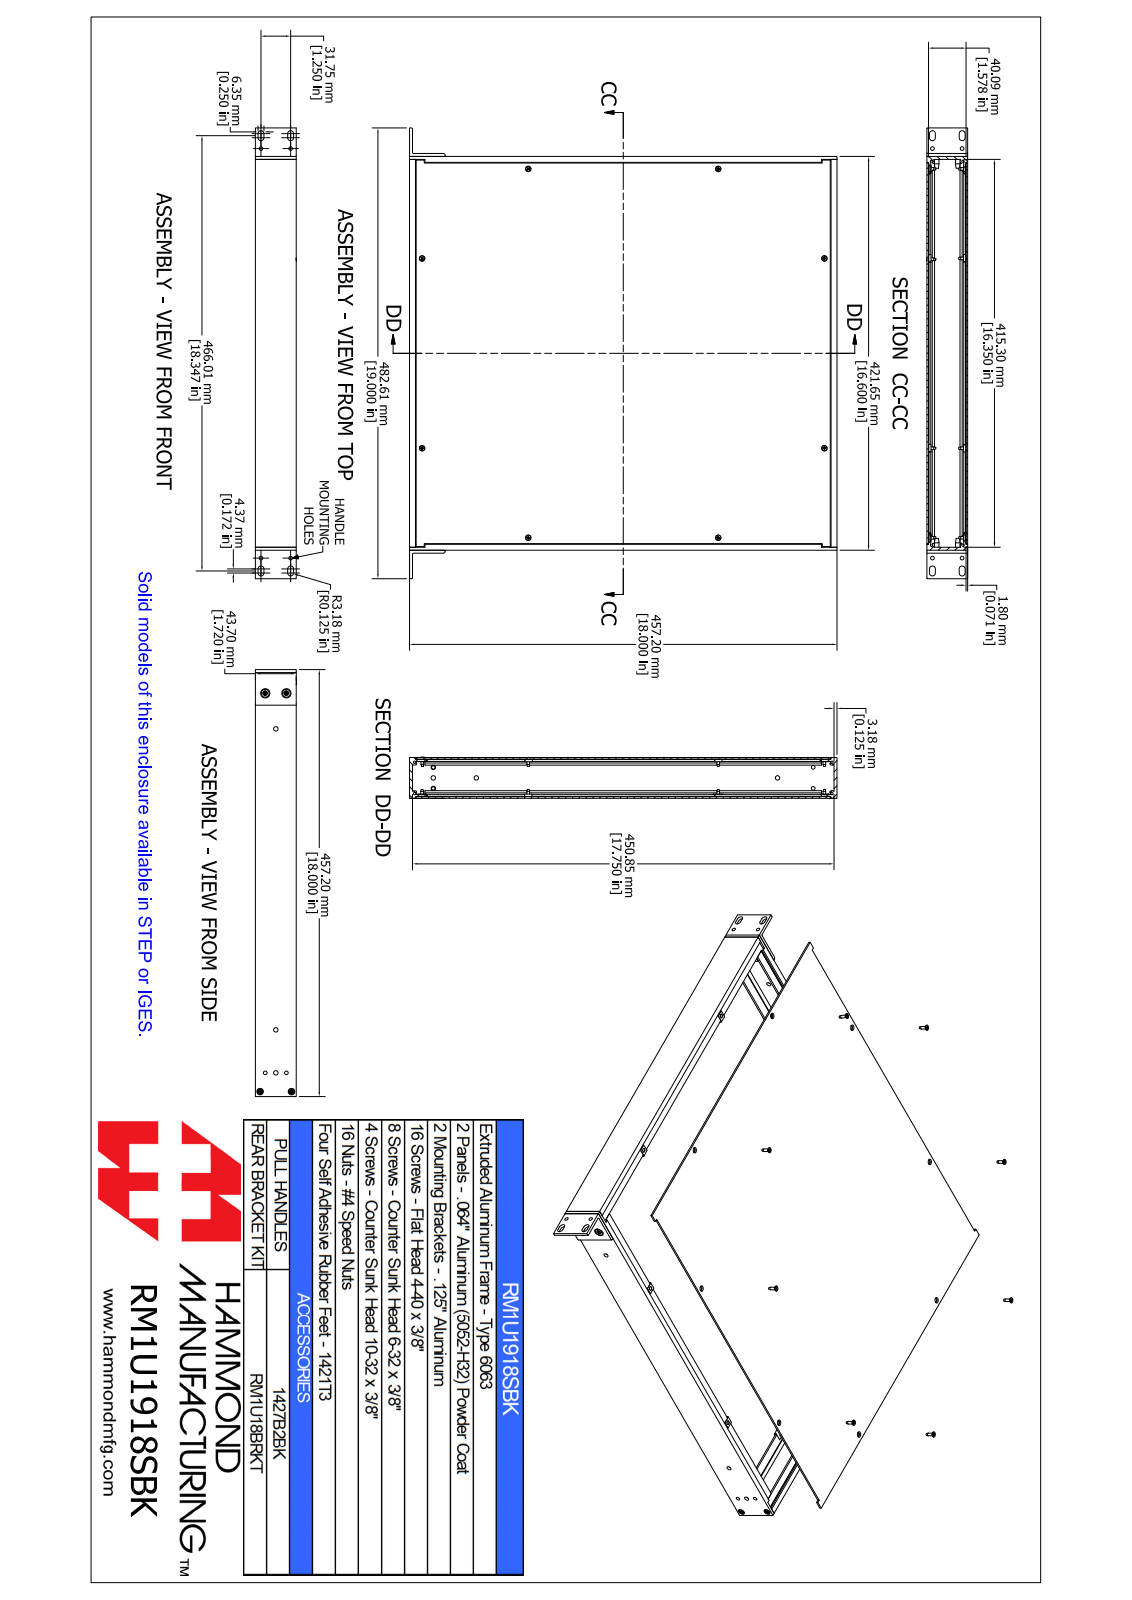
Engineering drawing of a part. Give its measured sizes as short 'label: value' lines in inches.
name: RM1U1918SBK
written by: SolidWorks 2021 (AUTOMOTIVE_DESIGN)
unit: in
bodies: 52 solids, 1358 faces (636 planar, 226 cylindrical, 496 other)
size: 19 × 18 × 1.735
volume: 64.6 in³; area: 1 597 in²
holes: 8× ⌀0.098, 8× ⌀0.157, 8× ⌀0.169, 6× ⌀0.188, 4× ⌀0.138, 4× ⌀0.156, 4× ⌀0.157, 2× ⌀0.197
bosses: 9× ⌀0.214, 9× ⌀0.112, 4× ⌀0.238, 4× ⌀0.138, 2× ⌀0.333, 2× ⌀0.19
rounds: 21× R0.039, 16× R0.125, 15× R0.049, 8× R0.05, 6× R0.038, 4× R0.037, 2× R0.079
face distances: 0.071, 1.649, 1.72, 1.578, 1.482, 0.167, 1.553, 0.096, 0.125, 0.125
hole spacings: 0.819, 1.565, 14.195, 14.507, 16.007, 16.792, 1.866, 0.445
